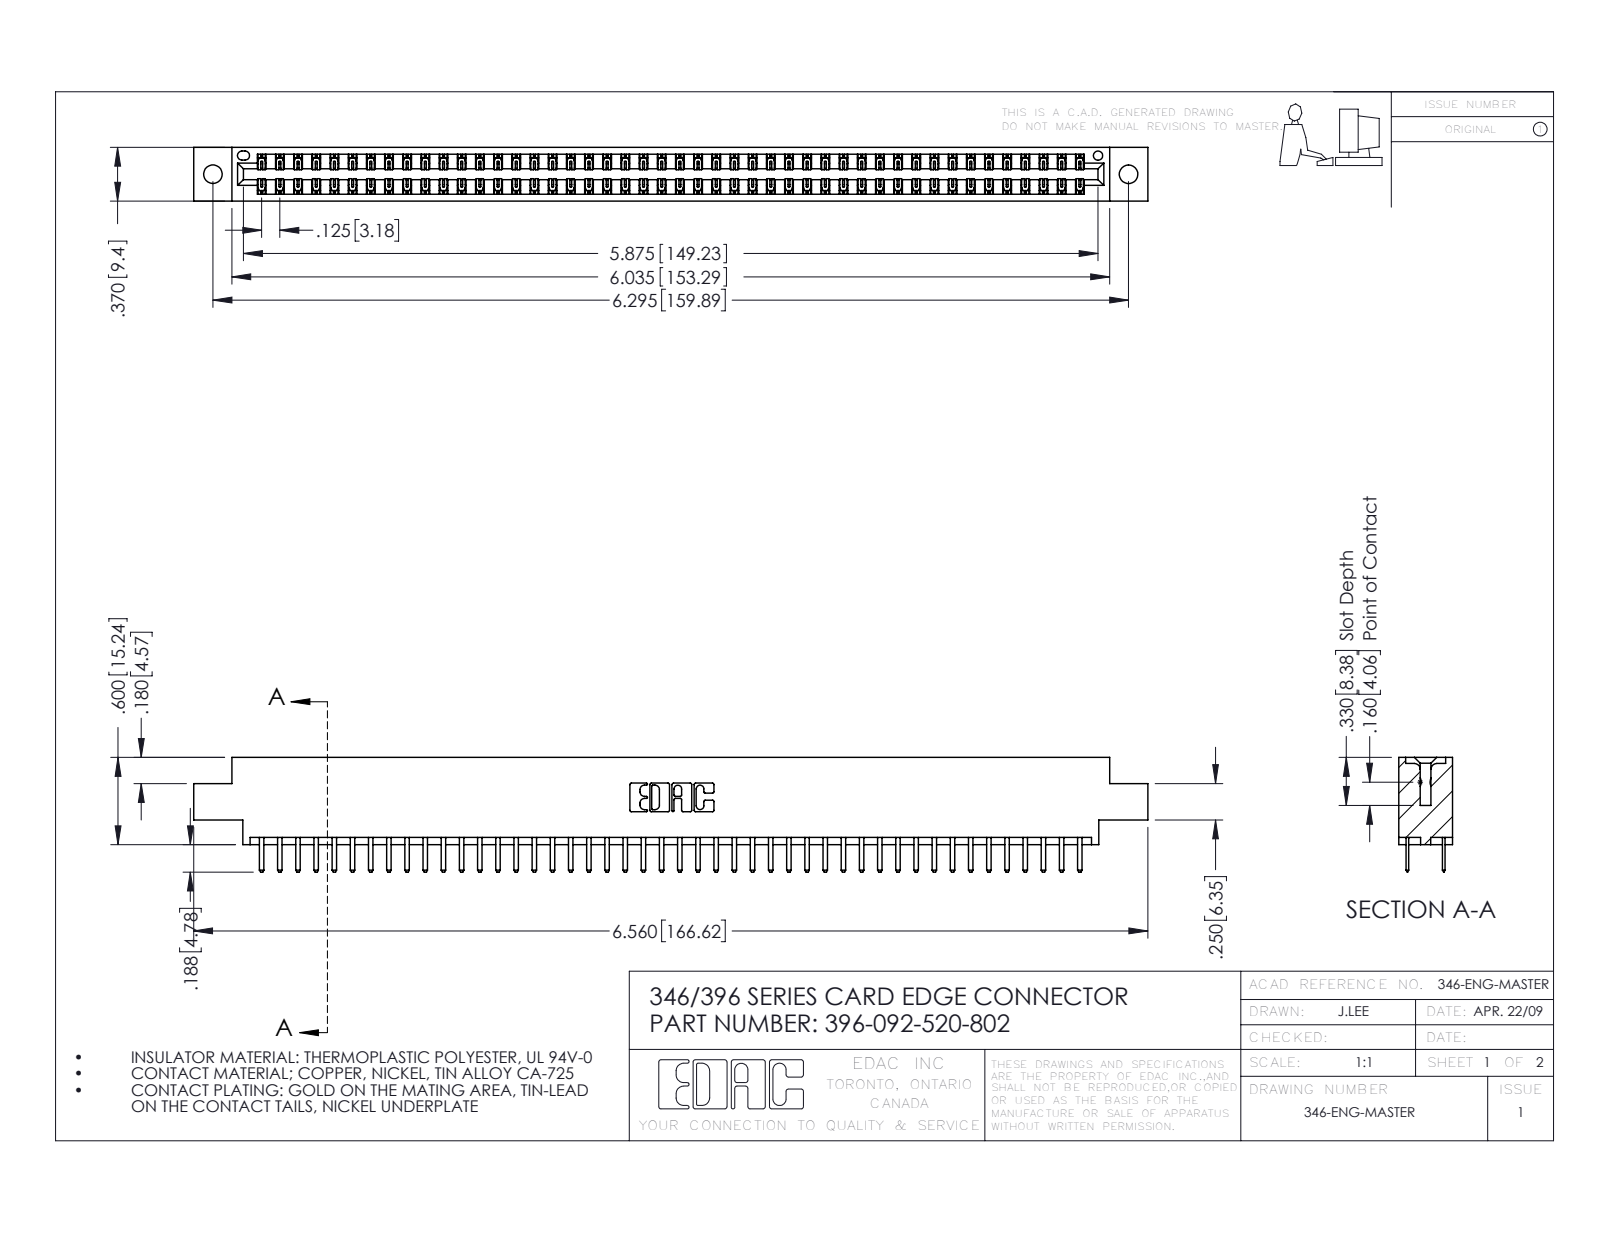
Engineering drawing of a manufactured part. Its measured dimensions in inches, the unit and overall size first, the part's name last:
Units: inches
Overall size (bounding box): 6.56 × 0.788 × 0.37
Round holes (diameter × count): ⌀0.128 ×2, ⌀0.064 ×1
Partial cylindrical surfaces — rounded edges, fillets, slot ends (radius × count): R0.006 ×138, R0.01 ×96, R0.01 ×22, R0.007 ×6, R0.031 ×6, R0.026 ×3, R0.014 ×2, R0.022 ×2
Main face-to-face distances: 0.048, 0.322, 0.25, 0.37, 0.275, 0.072, 0.298, 0.025, 0.148, 0.222
Hole centre spacings: 0.246, 6.086, 6.295
Volume: 0.979 in³ · Surface area: 34 in²
Bodies: 93 solids, 5278 faces (3484 planar, 1794 cylindrical, 0 other)
Part name (STEP PRODUCT): 396-092-520-802; 346 Part_0.170 Offset - 0.128 Dia; 345-292-001_345-293-120
STEP written by: SolidWorks 2016 (CONFIG_CONTROL_DESIGN)
